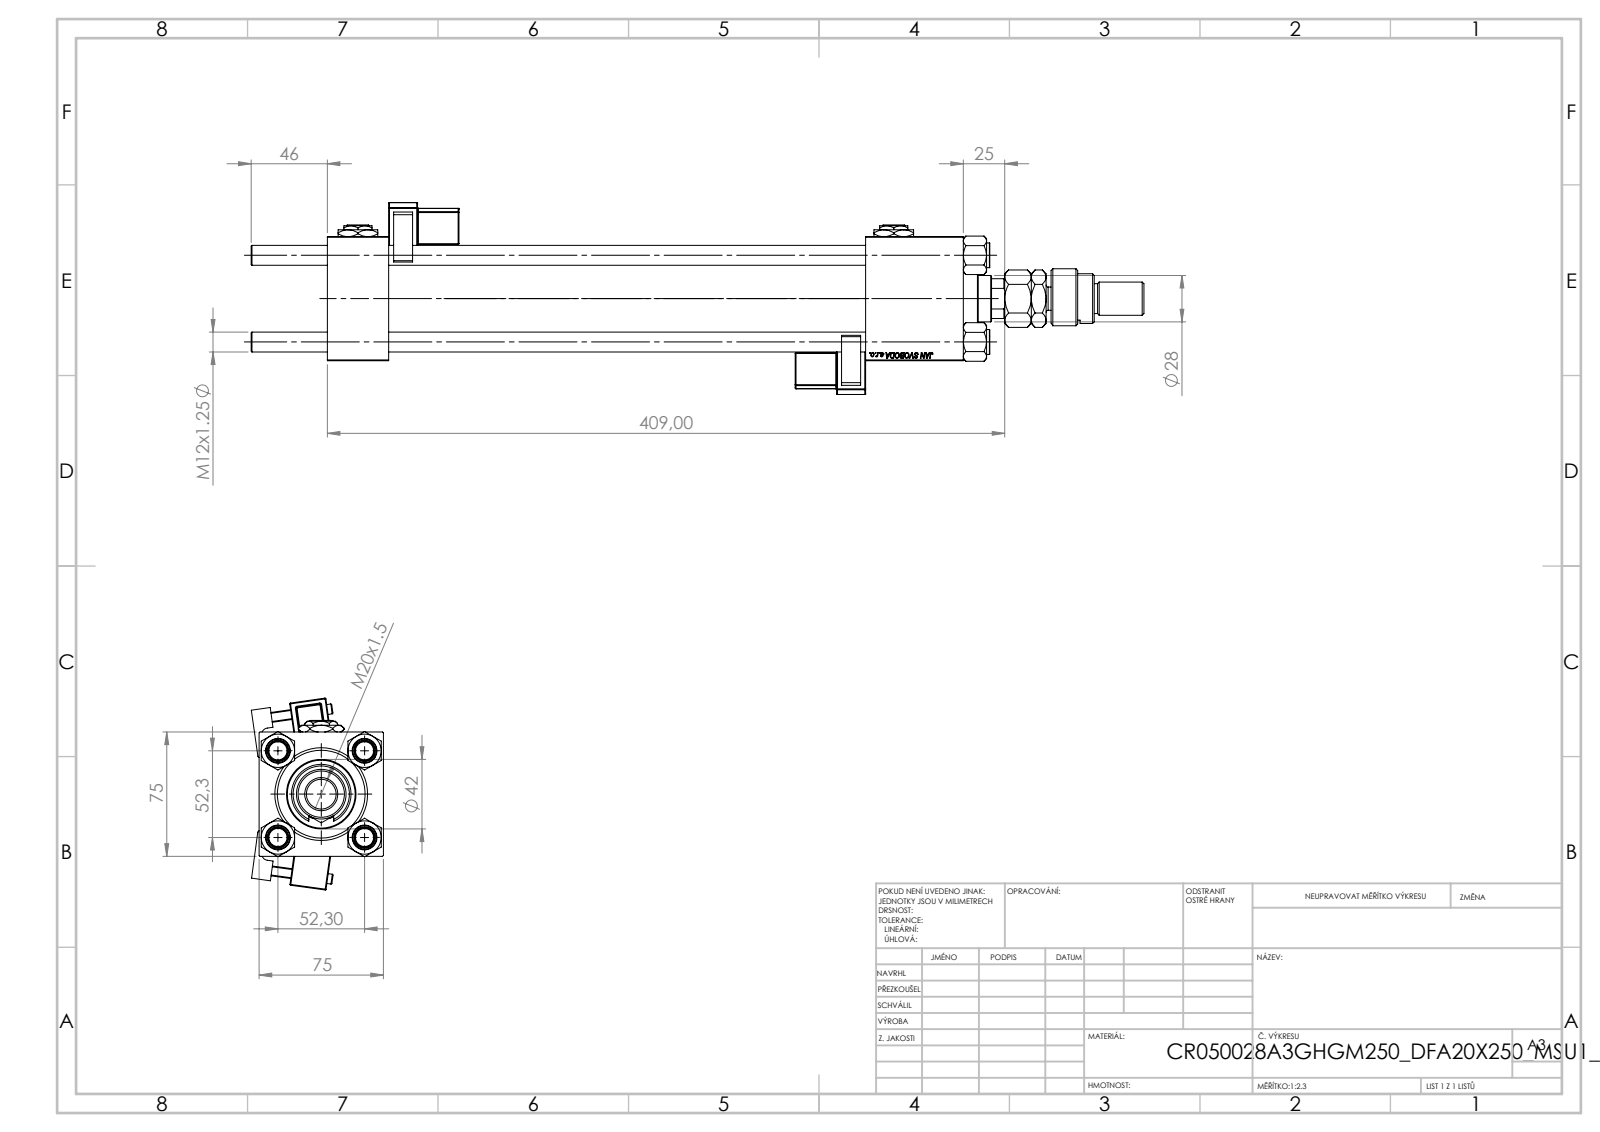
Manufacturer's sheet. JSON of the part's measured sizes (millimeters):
{"part_name": "V215CR_VCP; NUT_M5; V215CR_MSU; V215_VC_A (+5 more)", "step_written_by": "SolidWorks 2019 (CONFIG_CONTROL_DESIGN)", "units": "millimeters", "bodies": {"solids": 17, "faces": 1472, "planar": 653, "cylindrical": 161, "other": 658}, "overall_size": [539, 115.75, 79.69], "volume_mm3": 1148000, "surface_area_mm2": 328885, "round_holes": [[12, 4], [7, 2], [20.96, 2], [30, 2], [18.5, 1], [28, 1], [31, 1], [41, 1], [50, 1], [53, 1]], "round_bosses_or_shafts": [[15, 4], [6, 2], [56, 1], [42, 1], [36, 1], [30, 1], [22, 1], [20, 1]], "partial_cylinders_radius": [[0.5, 48], [1, 2], [2.5, 2], [4, 2], [7.5, 1], [12, 1], [13.5, 1]], "face_to_face_distances": [75, 37, 325, 384, 347, 59, 288, 355.3, 318.3, 30.3], "hole_center_spacings": [36.98, 52.3, 73.96, 323.5]}
